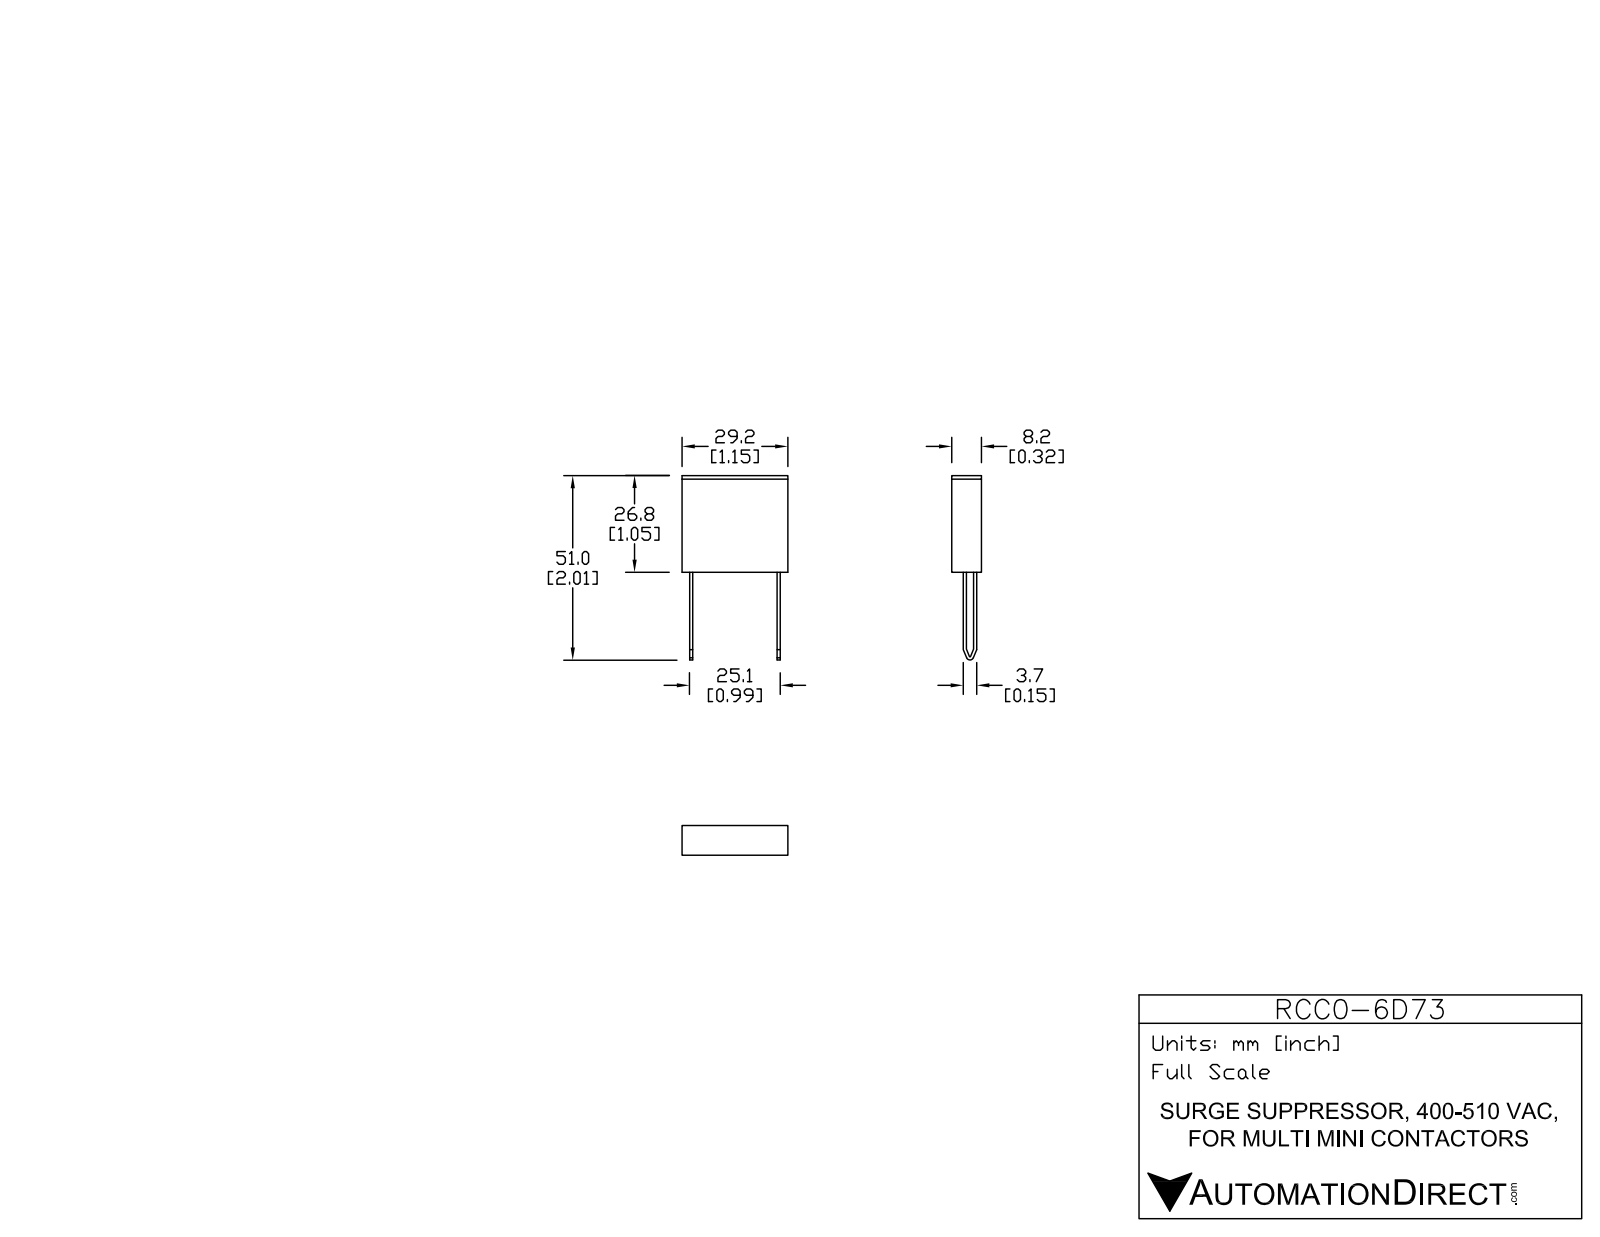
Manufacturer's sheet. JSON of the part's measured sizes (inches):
{"part_name": "RCC0-6D73", "step_written_by": "SolidWorks 2013 (AUTOMOTIVE_DESIGN)", "units": "inches", "bodies": {"solids": 1, "faces": 34, "planar": 26, "cylindrical": 8, "other": 0}, "overall_size": [2.004, 1.15, 0.323], "volume_in3": 0.394, "surface_area_in2": 4.345, "partial_cylinders_radius": [[0.006, 1], [0.039, 1]], "face_to_face_distances": [0.323, 1.051, 1.15, 0.033, 0.083, 1.067, 0.116, 1.033, 0.951, 0.112]}
